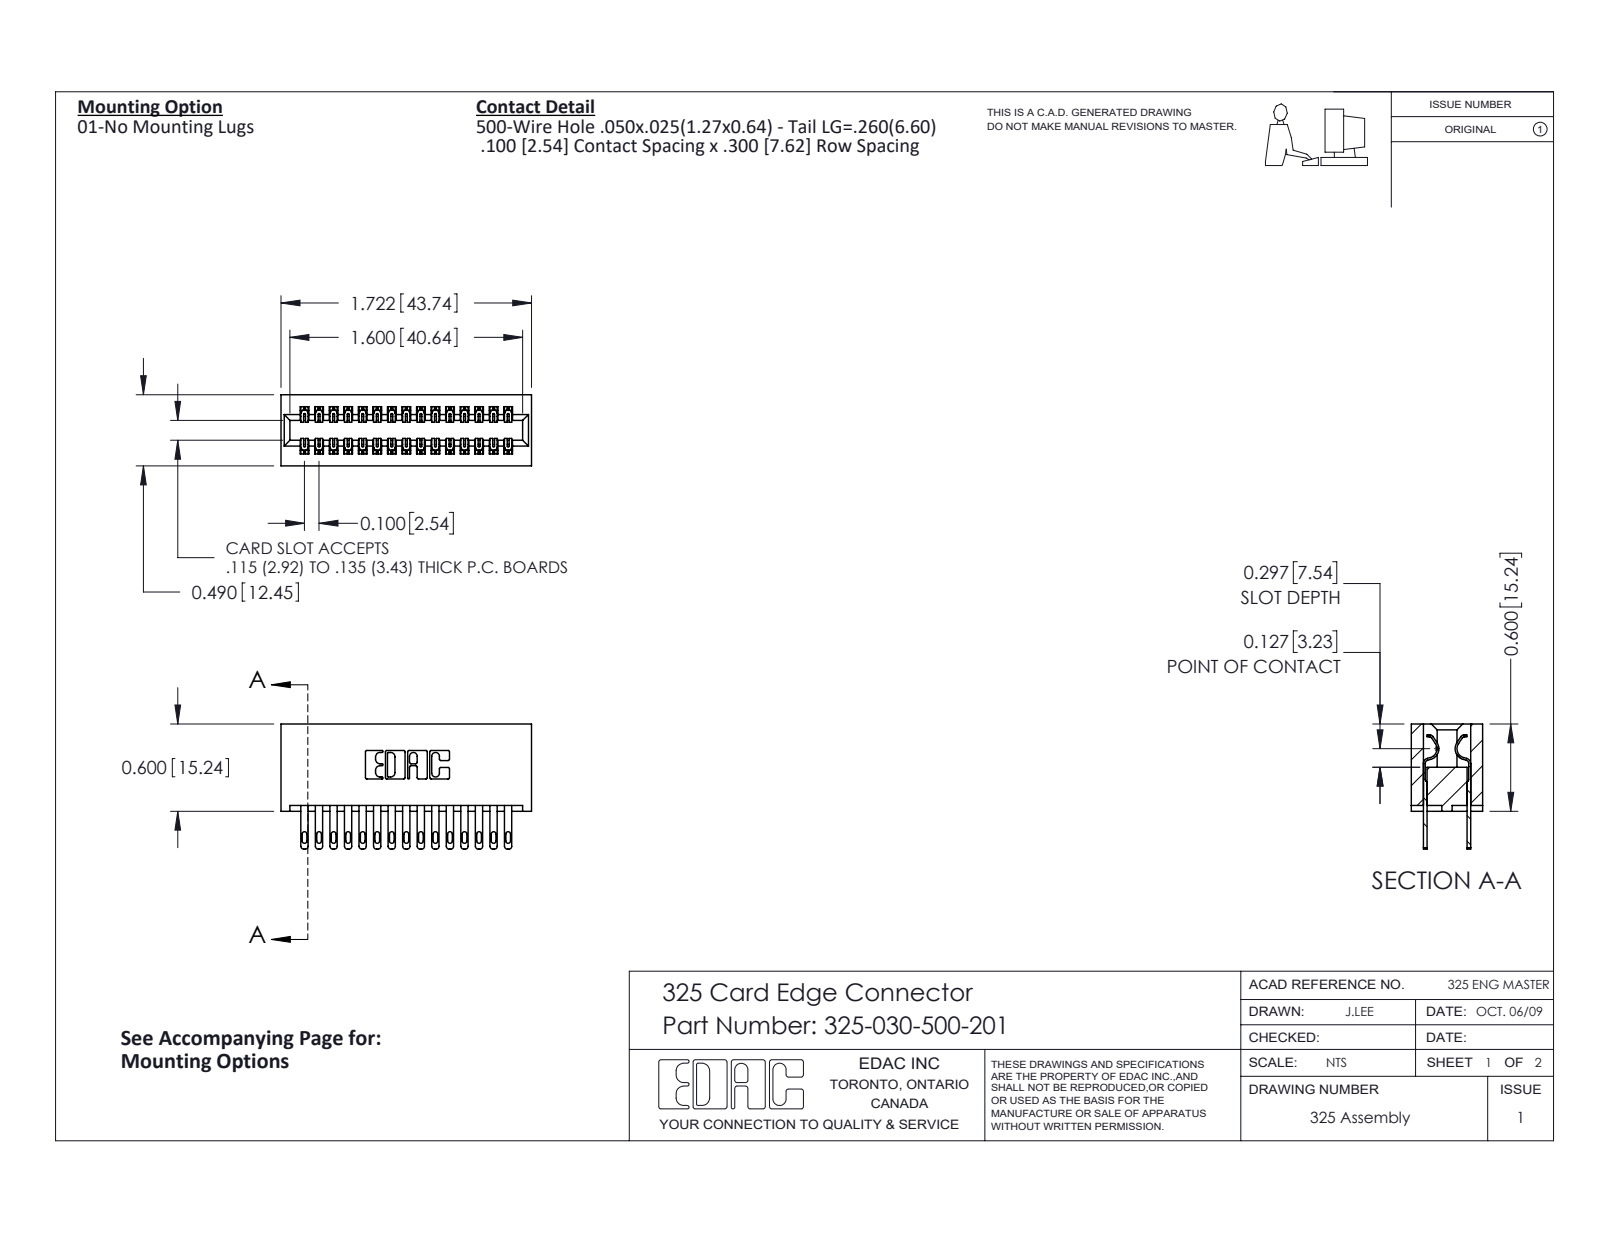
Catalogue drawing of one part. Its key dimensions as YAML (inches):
part_name: "325 Part_Lugless; 325-292-001_325-293-100; 325-030-500-201"
step_written_by: "SolidWorks 2016 (CONFIG_CONTROL_DESIGN)"
units: inches
bodies: {solids: 31, faces: 1546, planar: 966, cylindrical: 580, other: 0}
overall_size: [1.722, 0.86, 0.49]
volume: 0.372
surface_area: 11.97
partial_cylinders:
  - {radius: 0.006, count: 45}
  - {radius: 0.016, count: 30}
  - {radius: 0.02, count: 30}
  - {radius: 0.01, count: 22}
  - {radius: 0.007, count: 6}
  - {radius: 0.031, count: 6}
  - {radius: 0.026, count: 3}
  - {radius: 0.014, count: 2}
face_to_face_distances: [0.083, 0.407, 0.3, 0.107, 0.383, 0.025, 0.325, 0.49, 0.1, 0.2]
